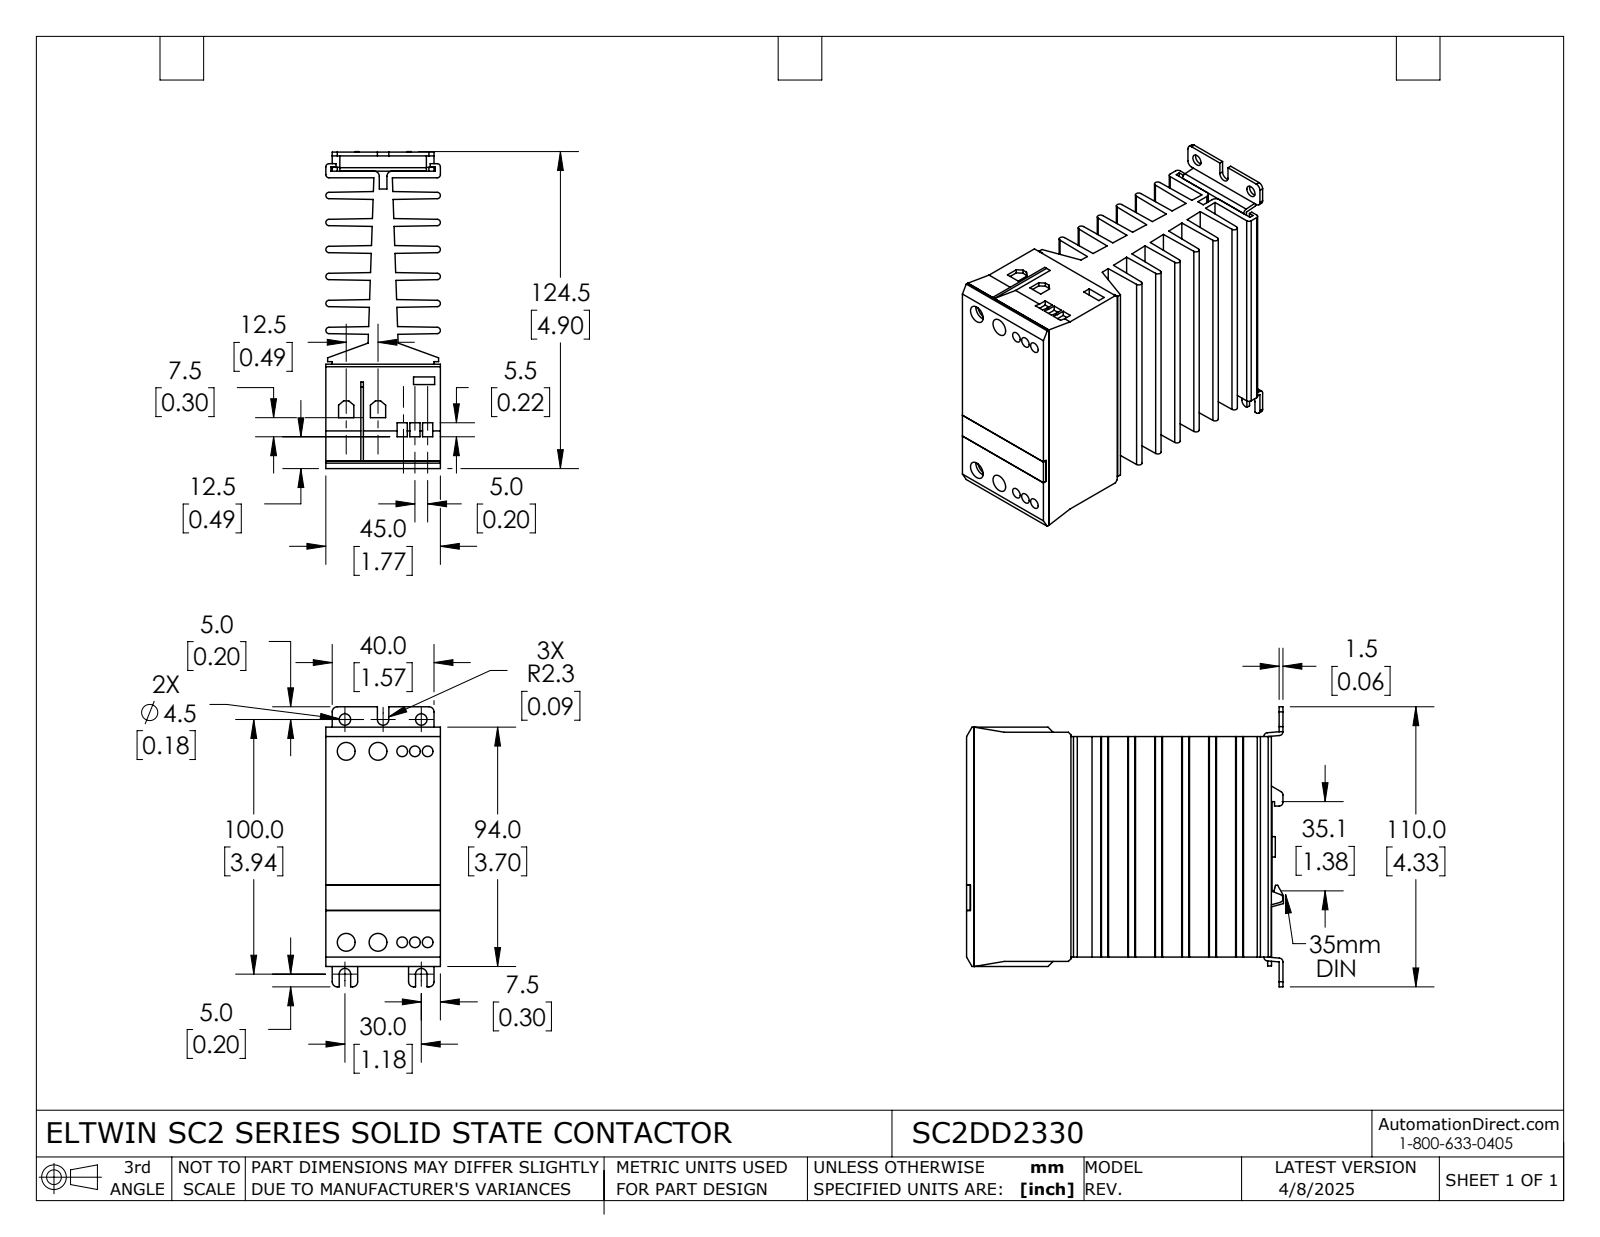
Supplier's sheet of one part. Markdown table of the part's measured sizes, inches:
| quantity | value |
| --- | --- |
| part name | SC2DD2330 |
| STEP written by | SolidWorks 2021 (AUTOMOTIVE_DESIGN) |
| units | inches |
| bodies | 7 solids, 391 faces (284 planar, 107 cylindrical, 0 other) |
| overall size | 4.902 × 4.331 × 1.772 |
| volume | 18.87 in³ |
| surface area | 165.4 in² |
| round holes (diameter × count) | 0.165 × 6, 0.173 × 6, 0.276 × 4, 0.177 × 2, 0.315 × 2 |
| round bosses / shafts (diameter × count) | 0.315 × 3 |
| partial cylindrical surfaces (radius × count) | 0.079 × 18, 0.049 × 16, 0.059 × 10, 0.051 × 4, 0.089 × 3 |
| main face-to-face distances | 0.417, 0.835, 0.127, 1.252, 0.29, 0.544, 0.707, 0.962, 1.669, 1.125 |
| hole center spacings | 2.953, 0.197, 2.959, 0.374, 0.394, 0.492, 0.502, 0.571 |
